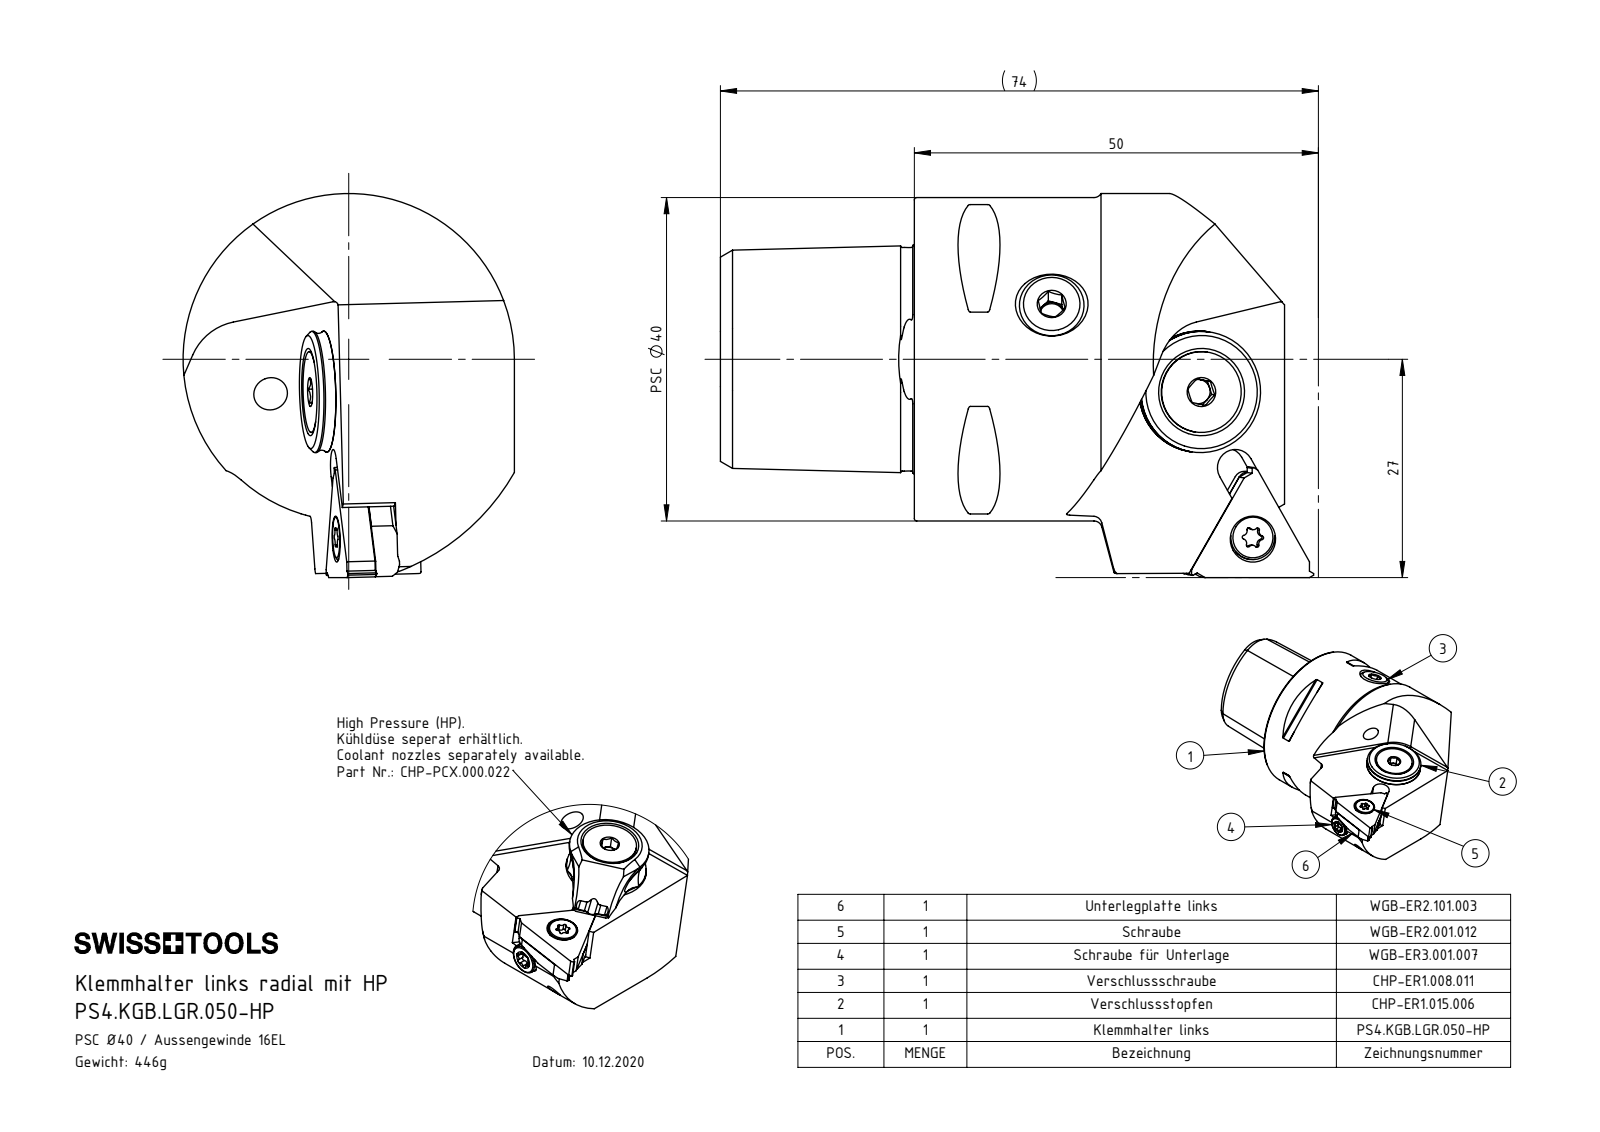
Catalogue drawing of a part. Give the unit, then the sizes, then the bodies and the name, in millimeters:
Units: millimetres
Overall size (bounding box): 73.41 × 47.5 × 41
Round holes (diameter × count): ⌀4.2 ×4, ⌀2.58 ×2, ⌀4 ×2, ⌀1.2 ×1, ⌀2 ×1, ⌀2.5 ×1, ⌀3 ×1, ⌀4.02 ×1, ⌀4.6 ×1, ⌀5.2 ×1, ⌀7 ×1, ⌀12.5 ×1
Round bosses / shafts (diameter × count): ⌀5.5 ×3, ⌀40 ×1, ⌀15 ×1, ⌀13.4 ×1, ⌀10 ×1, ⌀8 ×1, ⌀5 ×1, ⌀3.18 ×1
Partial cylindrical surfaces — rounded edges, fillets, slot ends (radius × count): R0.3 ×8, R0.23 ×6, R0.34 ×6, R0.57 ×6, R0.57 ×6, R0.1 ×2, R0.25 ×2, R0.5 ×2
Main face-to-face distances: 4.5, 1.16, 3.34, 24, 15.52, 4.81, 3.65, 0.31, 2.07, 3.23
Hole centre spacings: 4.5, 4.52, 4.53, 4.56, 16.81, 16.83, 16.85, 16.86
Volume: 56 386 mm³ · Surface area: 16 455 mm²
Bodies: 10 solids, 317 faces (127 planar, 84 cylindrical, 106 other)
Part name (STEP PRODUCT): ISO 8752 2x8; CHP-ER1.015.006_A; CHP-ER1.008.011_A; LT16EL (+8 more)
STEP written by: SolidWorks 2017 (AUTOMOTIVE_DESIGN)
